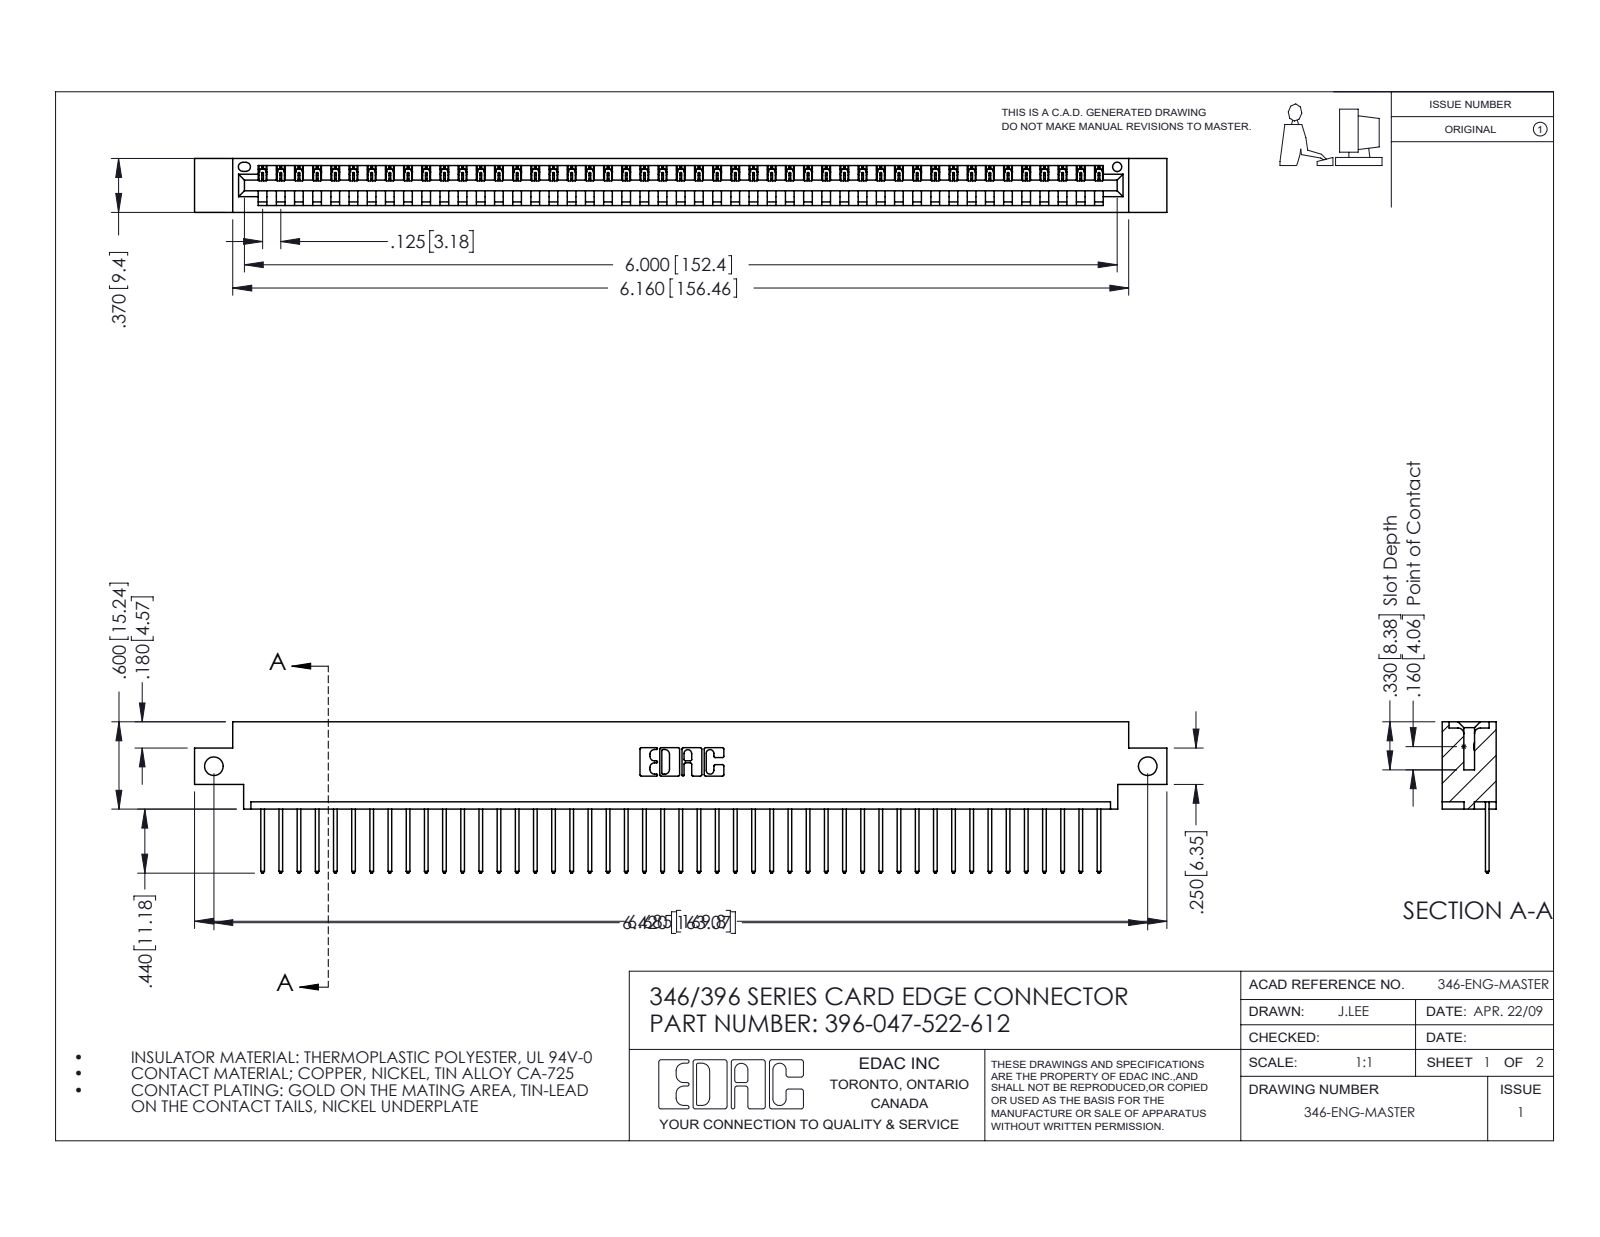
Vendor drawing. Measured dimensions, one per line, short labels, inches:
name: 346 Part_0.170 Offset - Side Mount; 396-047-522-612; 345-292-001_345-293-122
written by: SolidWorks 2016 (CONFIG_CONTROL_DESIGN)
unit: in
bodies: 48 solids, 2852 faces (1960 planar, 892 cylindrical, 0 other)
size: 6.685 × 1.04 × 0.37
volume: 0.98 in³; area: 31.47 in²
holes: 2× ⌀0.128, 1× ⌀0.064
rounds: 94× R0.006, 94× R0.01, 22× R0.01, 6× R0.007, 6× R0.031, 3× R0.026, 2× R0.031, 2× R0.04
face distances: 0.048, 0.322, 0.37, 0.25, 0.072, 0.298, 0.025, 0.148, 0.222, 0.1
hole spacings: 6.42
